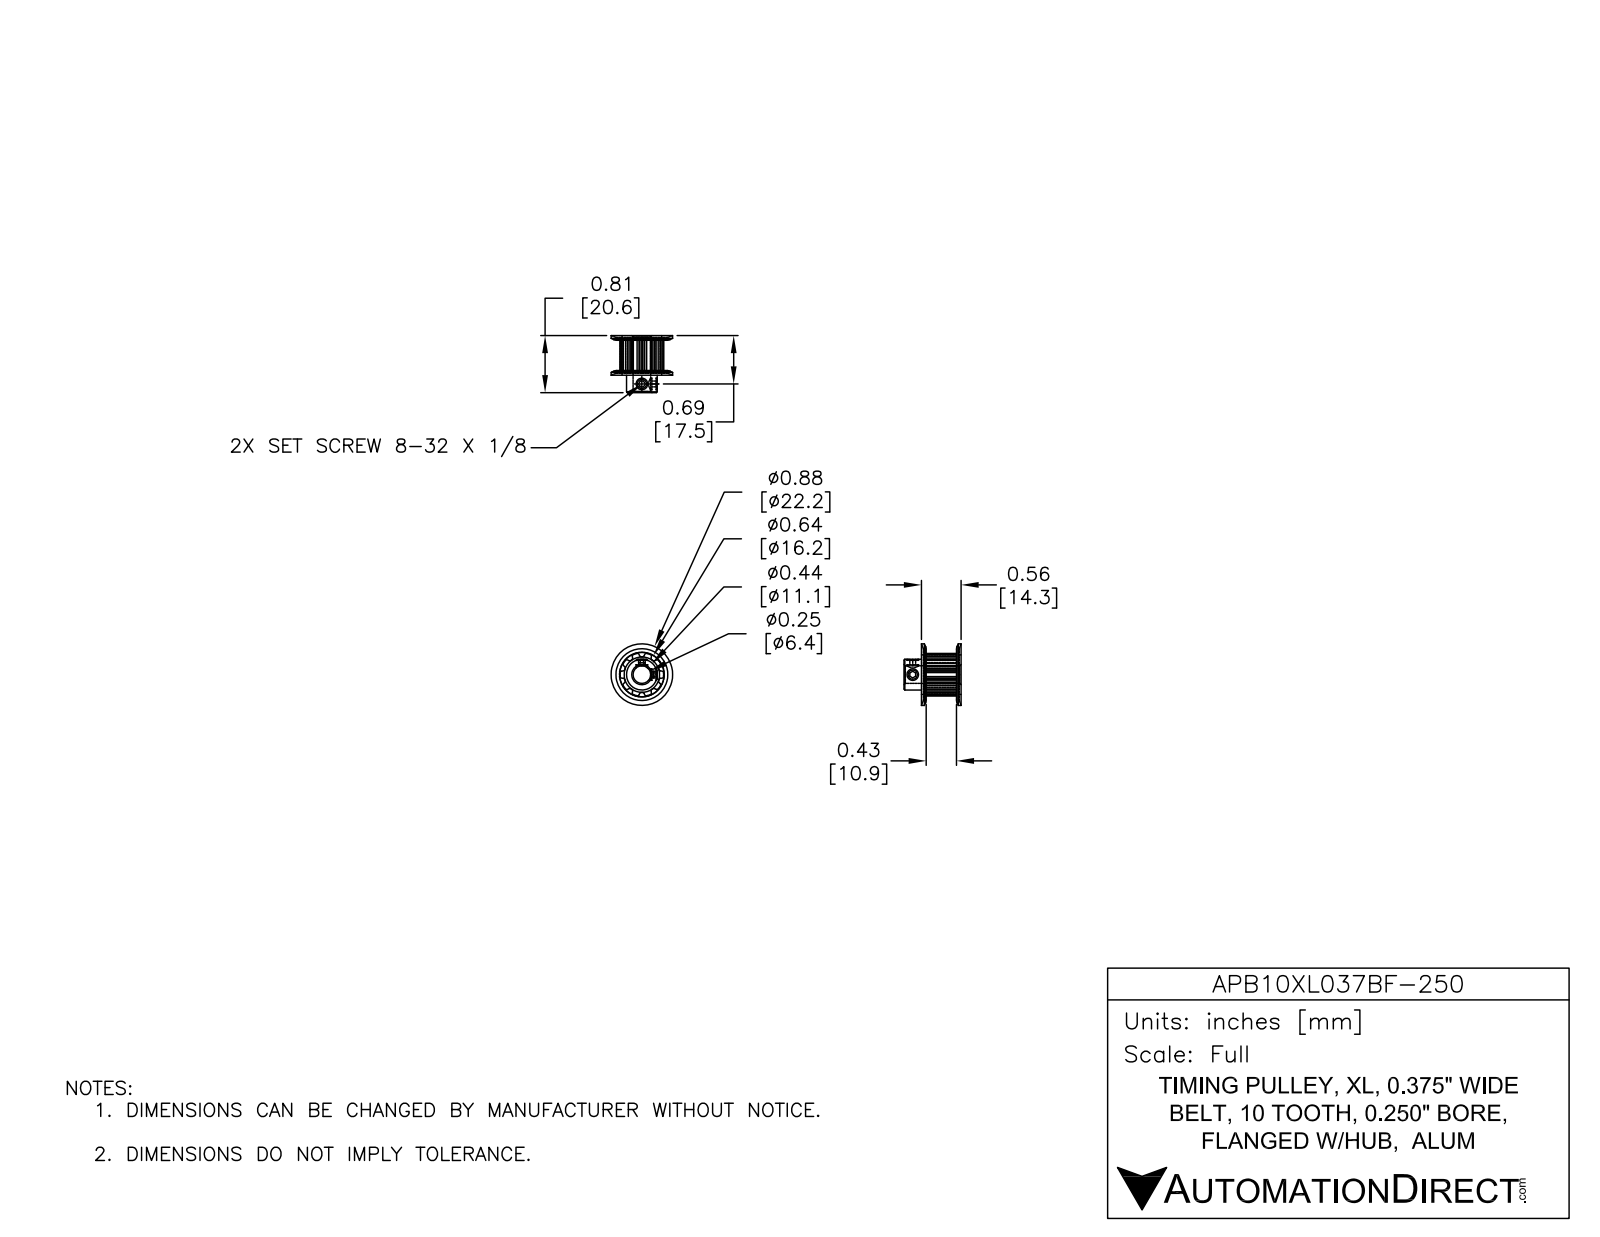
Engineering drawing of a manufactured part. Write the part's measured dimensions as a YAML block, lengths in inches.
part_name: "APB10XL037BF-250"
step_written_by: "SolidWorks 2014 (AUTOMOTIVE_DESIGN)"
units: inches
bodies: {solids: 1, faces: 125, planar: 36, cylindrical: 67, other: 22}
overall_size: [0.875, 0.875, 0.813]
volume: 0.156
surface_area: 4.114
round_holes:
  - {diameter: 0.088, count: 2}
  - {diameter: 0.25, count: 1}
round_bosses_or_shafts:
  - {diameter: 0.438, count: 1}
partial_cylinders:
  - {radius: 0.015, count: 40}
  - {radius: 0.254, count: 1}
face_to_face_distances: [0.495, 0.166, 0.033, 0.617, 0.528, 0.813, 0.78, 0.285, 0.065, 0.032]
